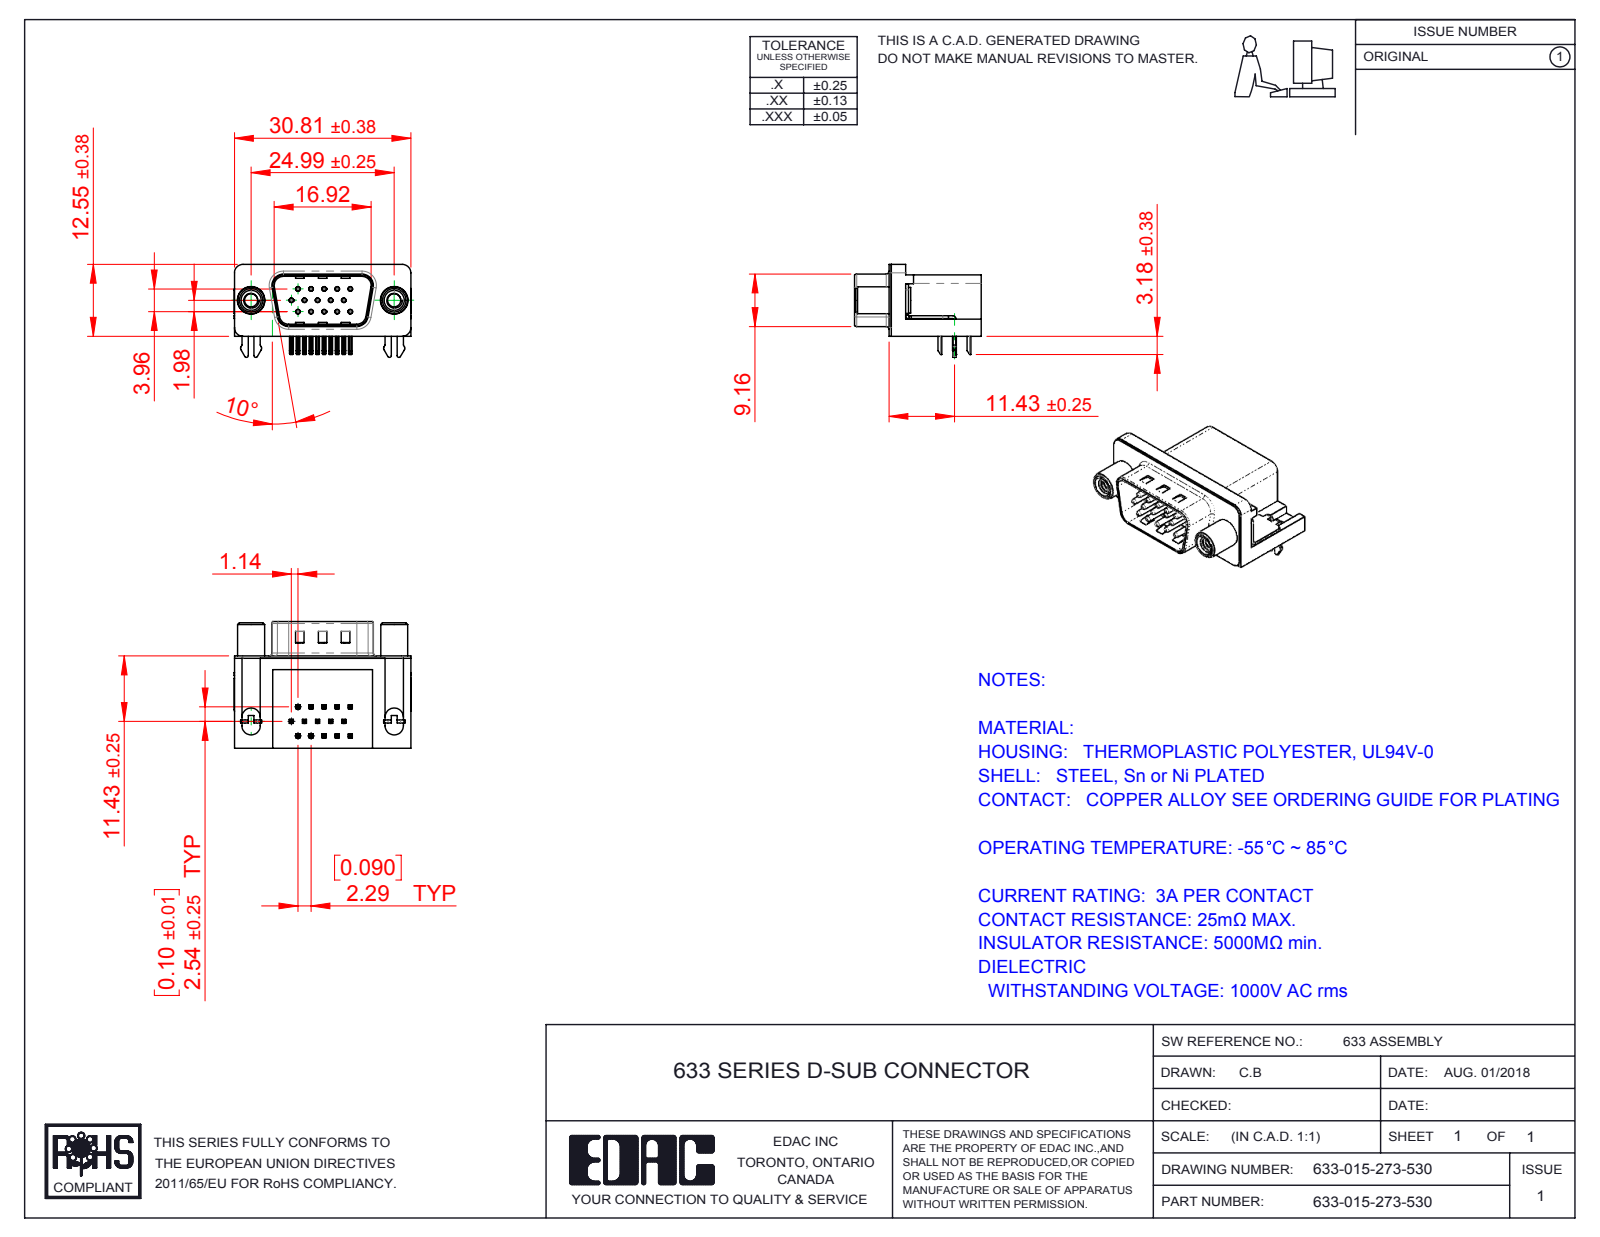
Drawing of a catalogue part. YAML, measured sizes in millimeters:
part_name: "633 Contact Middle_Recessed; 633 Round Threaded Standoff; 633-015-273-530; 633 Contact Middle (+5 more)"
step_written_by: "SolidWorks 2016 (CONFIG_CONTROL_DESIGN)"
units: millimeters
bodies: {solids: 21, faces: 1477, planar: 885, cylindrical: 459, other: 133}
overall_size: [30.89, 22.1, 16.25]
volume: 4163
surface_area: 5625
round_holes:
  - {diameter: 0.35, count: 15}
  - {diameter: 0.8, count: 15}
  - {diameter: 2.3, count: 2}
  - {diameter: 3.1, count: 2}
  - {diameter: 4, count: 2}
  - {diameter: 4.8, count: 2}
  - {diameter: 5, count: 2}
round_bosses_or_shafts:
  - {diameter: 0.75, count: 15}
  - {diameter: 4.9, count: 2}
  - {diameter: 4.7, count: 2}
  - {diameter: 4.5, count: 2}
  - {diameter: 3.85, count: 2}
partial_cylinders:
  - {radius: 0.25, count: 60}
  - {radius: 0.12, count: 30}
  - {radius: 1, count: 16}
  - {radius: 0.5, count: 14}
  - {radius: 1.6, count: 8}
  - {radius: 1.5, count: 7}
  - {radius: 0.32, count: 4}
  - {radius: 0.9, count: 4}
face_to_face_distances: [0.4, 10.35, 15.7, 2.9, 6.7, 2.5, 16.1, 0.5, 0.35, 10.7]
hole_center_spacings: [3.96, 2.28, 4.57, 2.29, 6.05, 6.86, 7.92, 6.04]
